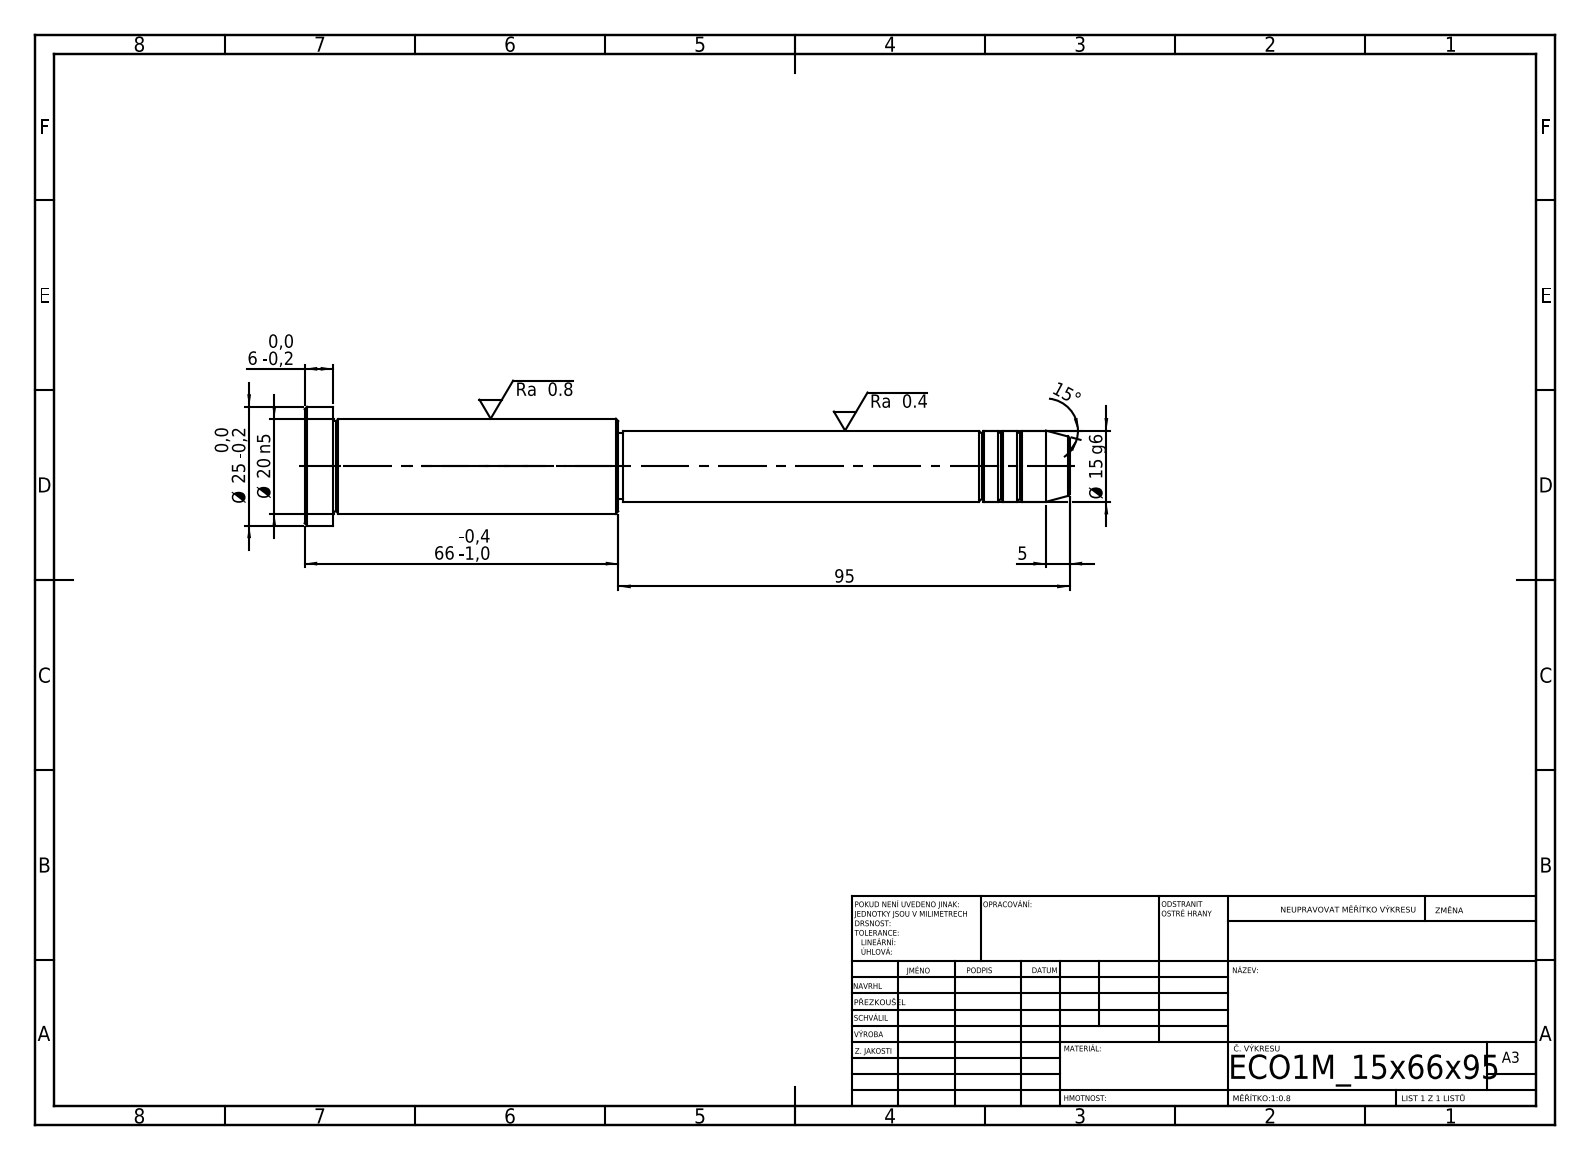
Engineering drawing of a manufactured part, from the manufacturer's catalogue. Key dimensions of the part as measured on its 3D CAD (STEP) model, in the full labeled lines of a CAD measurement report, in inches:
STEP written by: SolidWorks 2019 (CONFIG_CONTROL_DESIGN)
Units: inches
Bodies: 1 solid, 43 faces (5 planar, 14 cylindrical, 24 other)
Overall size (bounding box): 6.339 × 0.984 × 0.984
Volume: 2.338 in³ · Surface area: 15.08 in²
Round bosses / shafts (diameter × count): ⌀0.984 ×1, ⌀0.787 ×1, ⌀0.591 ×1, ⌀0.551 ×1
Main face-to-face distances: 0.236, 2.362, 2.598, 3.74, 6.102, 6.339, 3.701, 0.039, 2.402, 2.638
